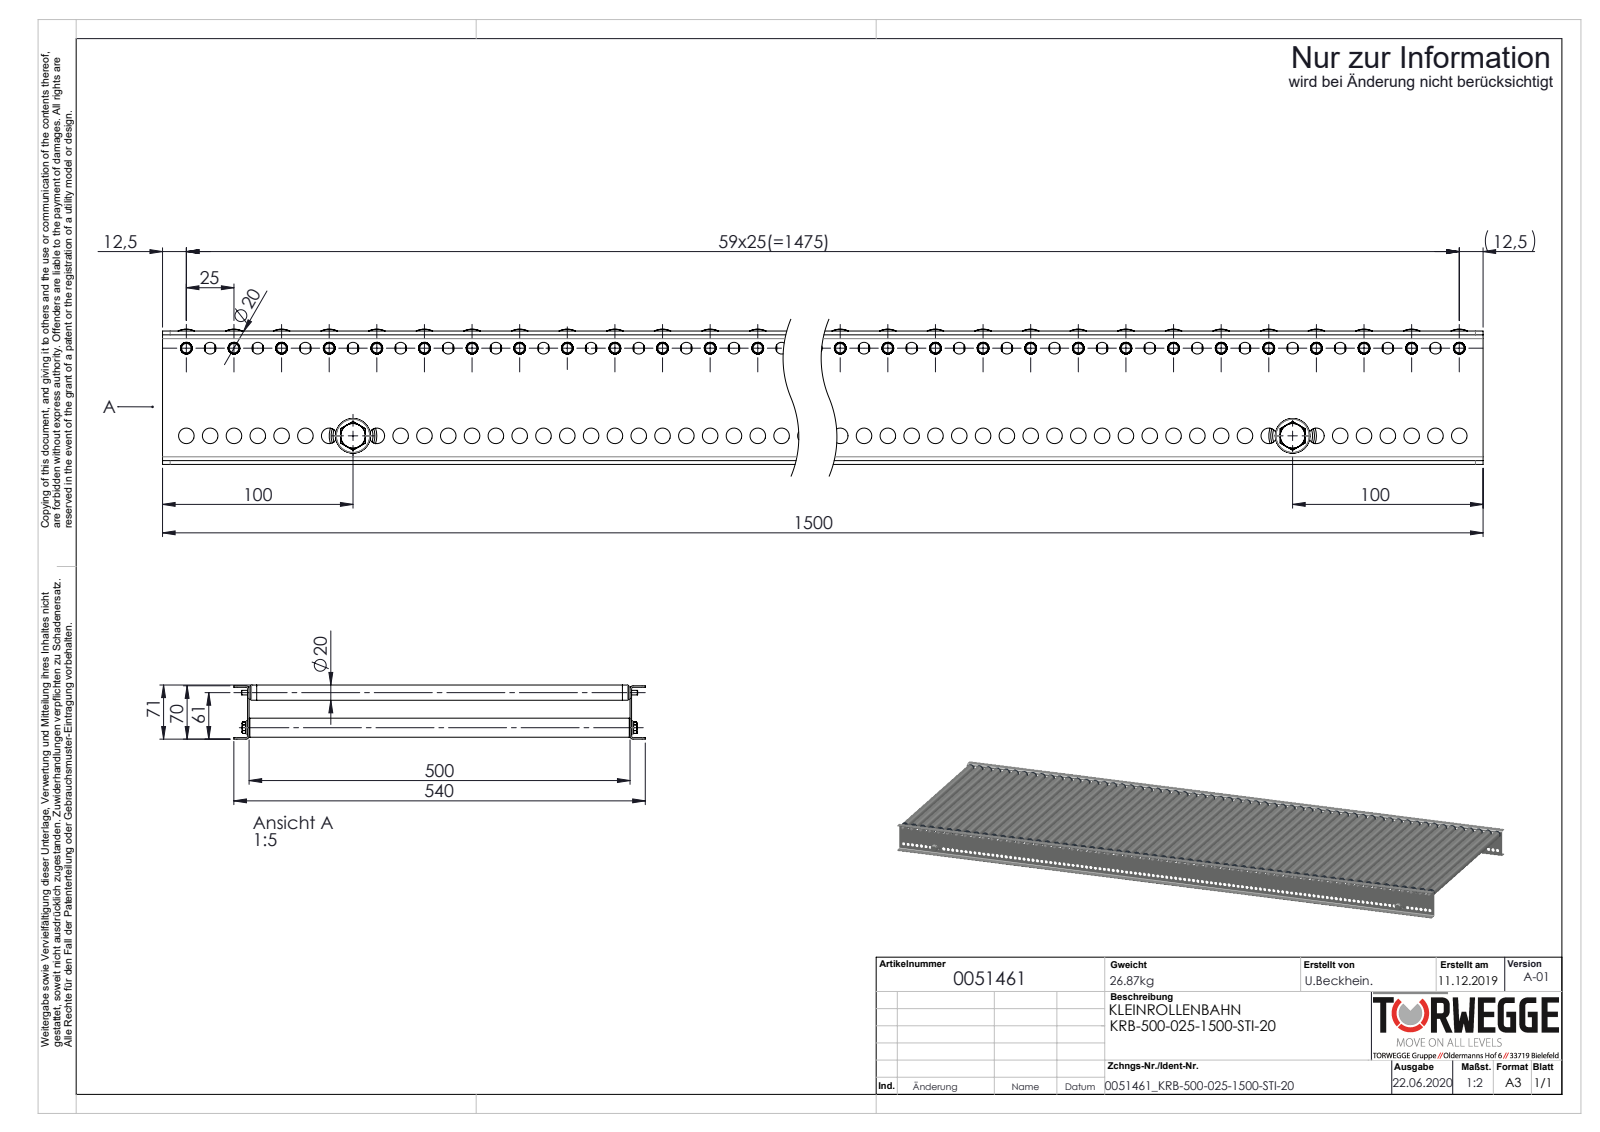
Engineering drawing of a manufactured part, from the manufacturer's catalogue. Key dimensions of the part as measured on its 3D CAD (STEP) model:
Part name (STEP PRODUCT): Profil_KRB-20x70x20x2_KFG_S100205_U-PROFIL-20-70-20-2-KRB-20-L=1500; 0051461; S100994_Sperrzahnschraube_M08x16-8.8-A2K; KUT50-20x1,5-STI-A6_FA-EL=KFG_S100911_KUT50-20x1-STI-A6-FA-EL=500 (+4 more)
STEP written by: SolidWorks 2020 (AUTOMOTIVE_DESIGN)
Units: millimetres
Bodies: 132 solids, 11792 faces (3840 planar, 4488 cylindrical, 3464 other)
Overall size (bounding box): 1500 × 540 × 71
Volume: 3 355 000 mm³ · Surface area: 5 192 000 mm²
Round holes (diameter × count): ⌀6.2 ×119, ⌀8.2 ×119, ⌀6.1 ×60, ⌀14.2 ×60, ⌀17.2 ×60, ⌀18 ×60, ⌀6.8 ×2, ⌀21 ×2
Round bosses / shafts (diameter × count): ⌀20 ×60, ⌀19.9 ×60, ⌀18.1 ×60, ⌀17.8 ×60, ⌀16.5 ×60, ⌀6 ×60, ⌀25 ×2, ⌀8 ×2
Partial cylindrical surfaces — rounded edges, fillets, slot ends (radius × count): R4.05 ×60, R4 ×8, R2 ×4
Main face-to-face distances: 2, 502, 68, 500, 504, 70, 66, 492, 18, 30
Hole centre spacings: 12.5, 25, 37.5, 50, 62.5, 75, 87.5, 100
